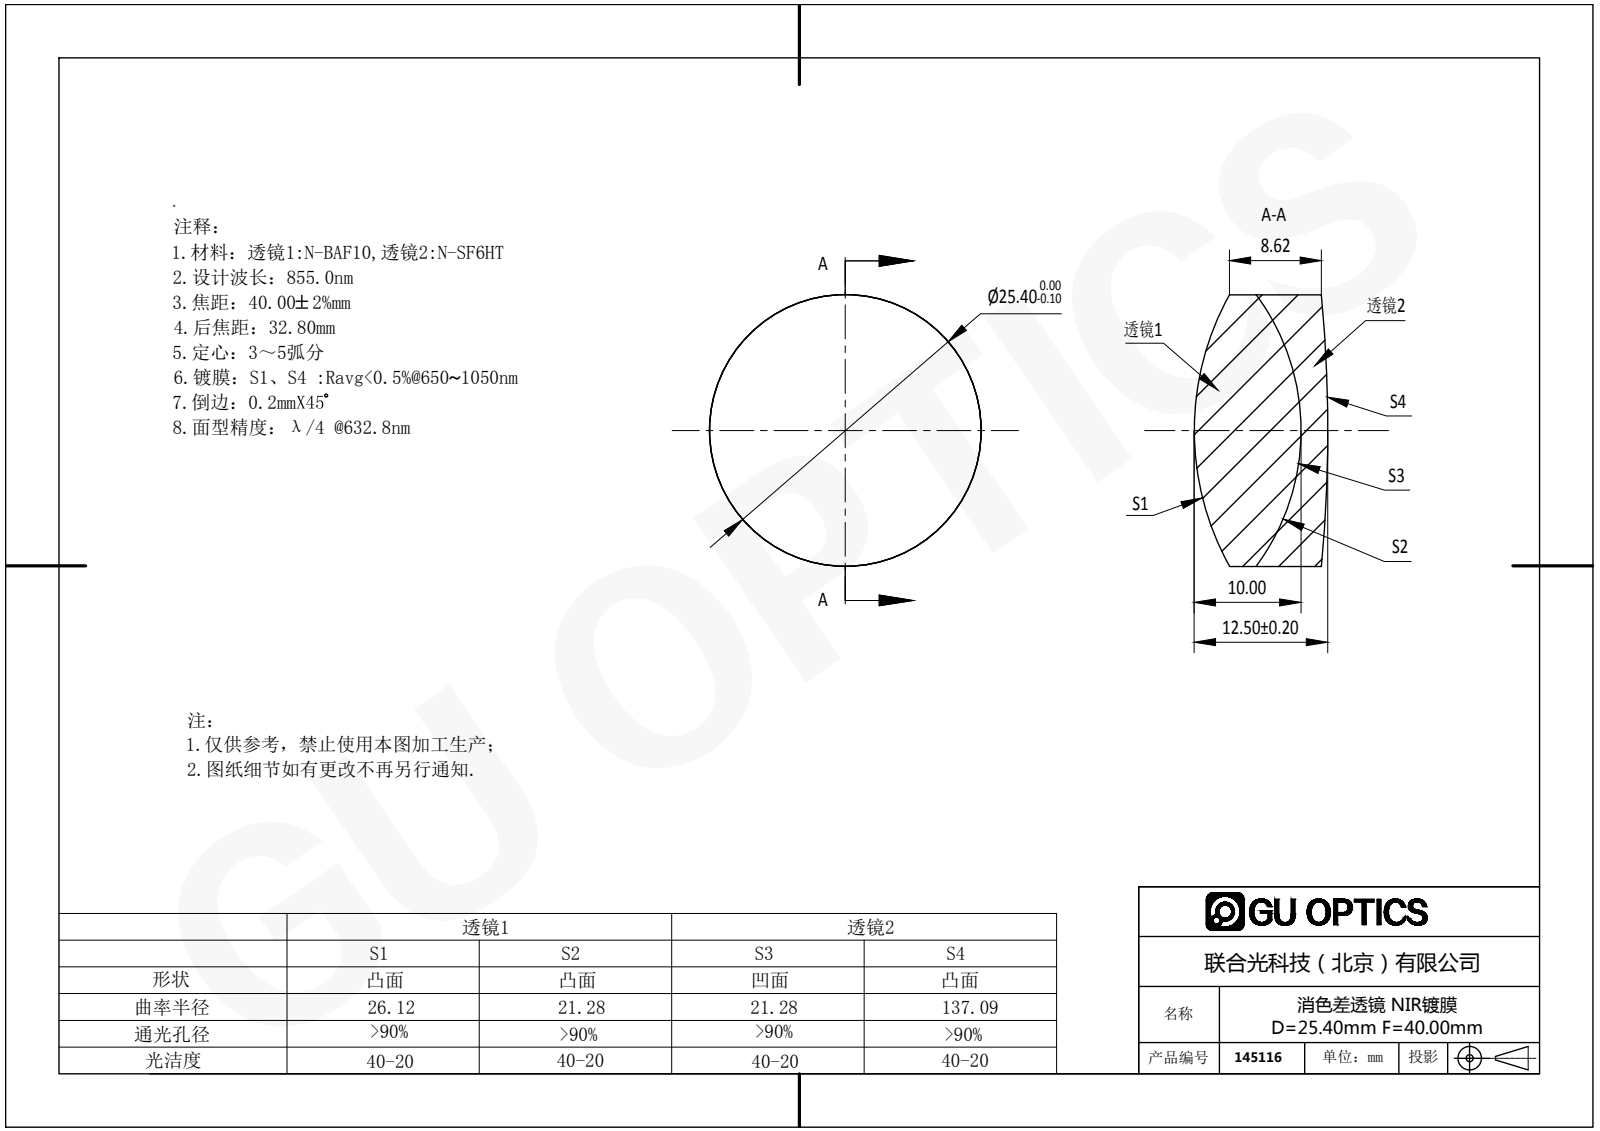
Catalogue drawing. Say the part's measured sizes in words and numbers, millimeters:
The part is named "145116". Its 3-D file was written by "SolidWorks 2016 (AUTOMOTIVE_DESIGN)". It is 2 solids with 12 faces: 0 planar, 4 cylindrical and 8 other. Overall it measures 25.4 by 25.4 by 12.5 millimeters. Its volume is 5 368 cubic millimeters and its surface area 2 861 square millimeters. Round bosses or shafts: 1 of diameter 25.4.
